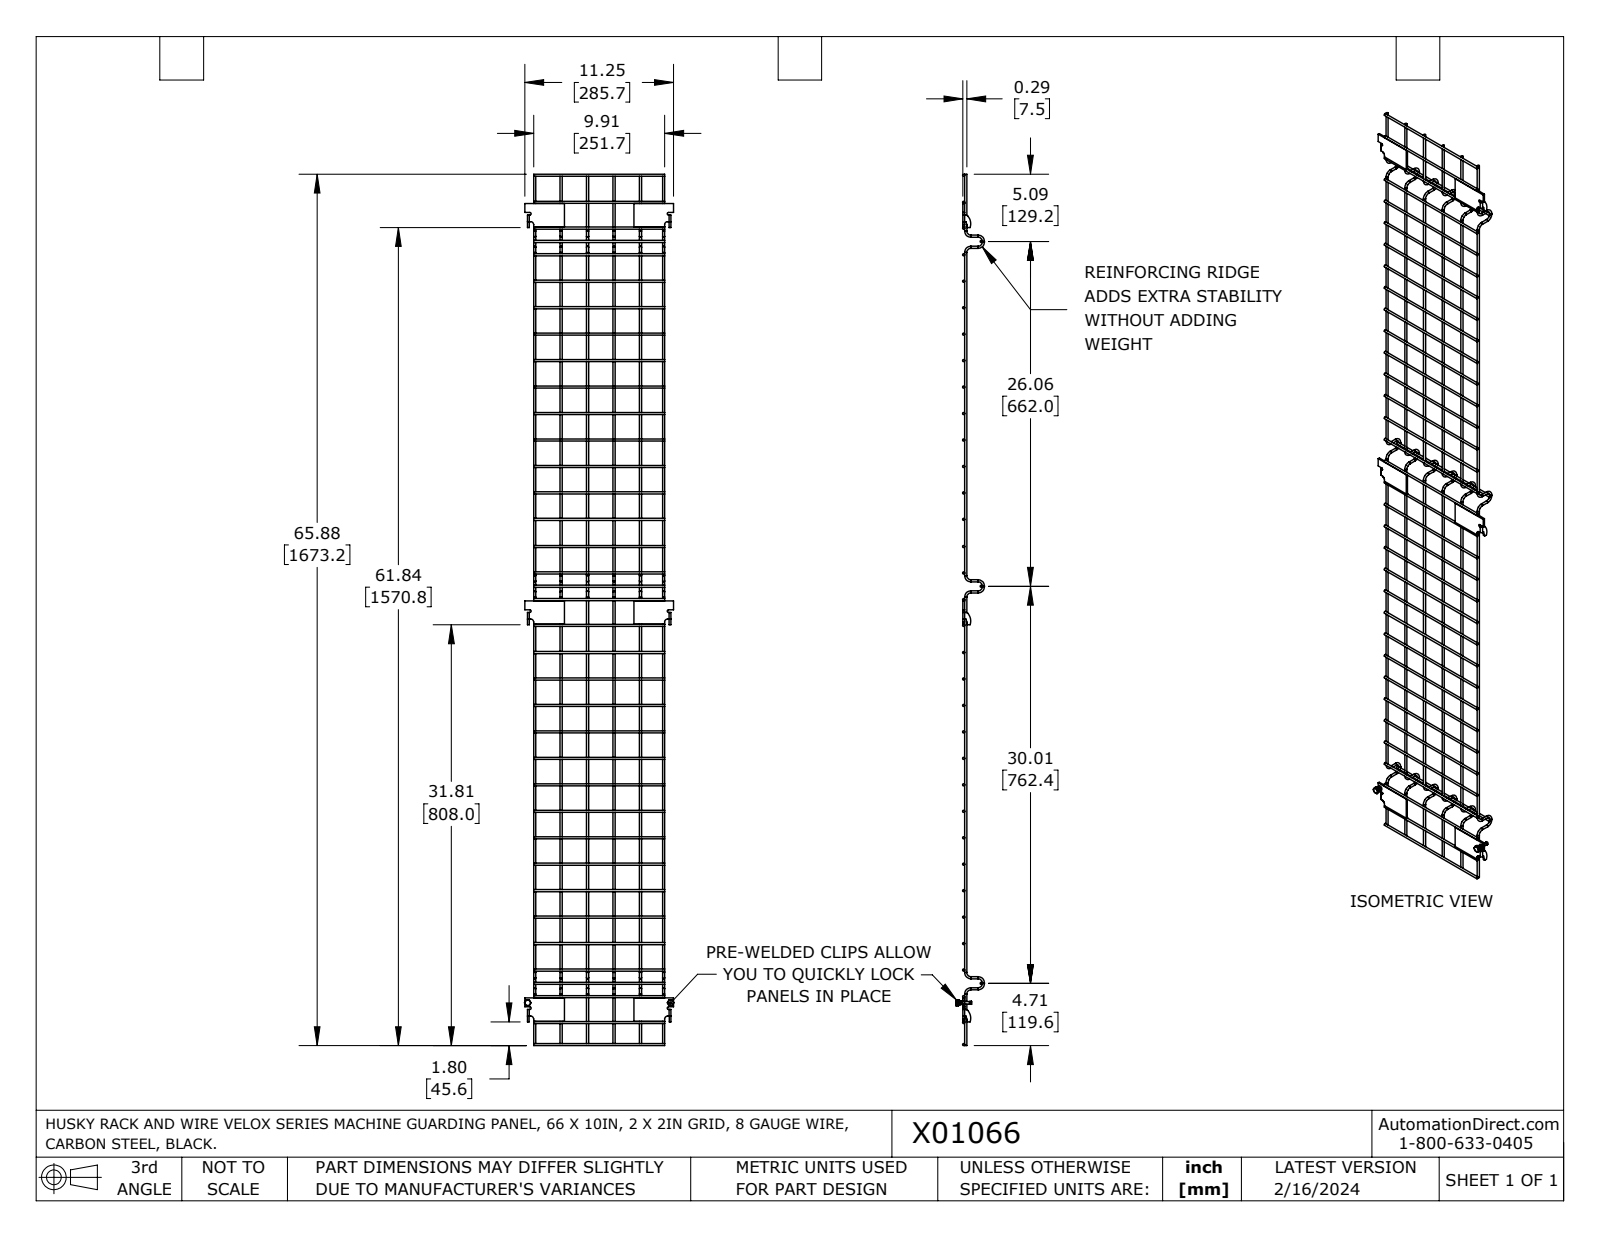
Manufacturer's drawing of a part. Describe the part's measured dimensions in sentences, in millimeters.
The part is named "X01066". Its 3-D file was written by "SolidWorks 2023 (AUTOMOTIVE_DESIGN)". It is 53 solids with 453 faces: 194 planar, 163 cylindrical and 96 other. Overall it measures 1673.2 by 287.4 by 53.4 millimeters. Its volume is 330 900 cubic millimeters and its surface area 307 400 square millimeters. Round holes: 2 of diameter 5.1, 2 of diameter 6.4. Round bosses or shafts: 85 of diameter 4.1, 2 of diameter 9.9, 2 of diameter 6.2, 2 of diameter 4.7. Partial cylindrical surfaces (rounded edges, fillets, slot ends): 6 of radius 2.5, 6 of radius 5.5, 3 of radius 6.4, 3 of radius 22, 2 of radius 0.2, 2 of radius 1.7, 2 of radius 3.4. The main face-to-face distances are 3.4, 3.2, 44.8, 762.8, 11.9, 263.6, 762.4, 1525.2, 71.1, 204.4. The hole center spacings are 274.5.
